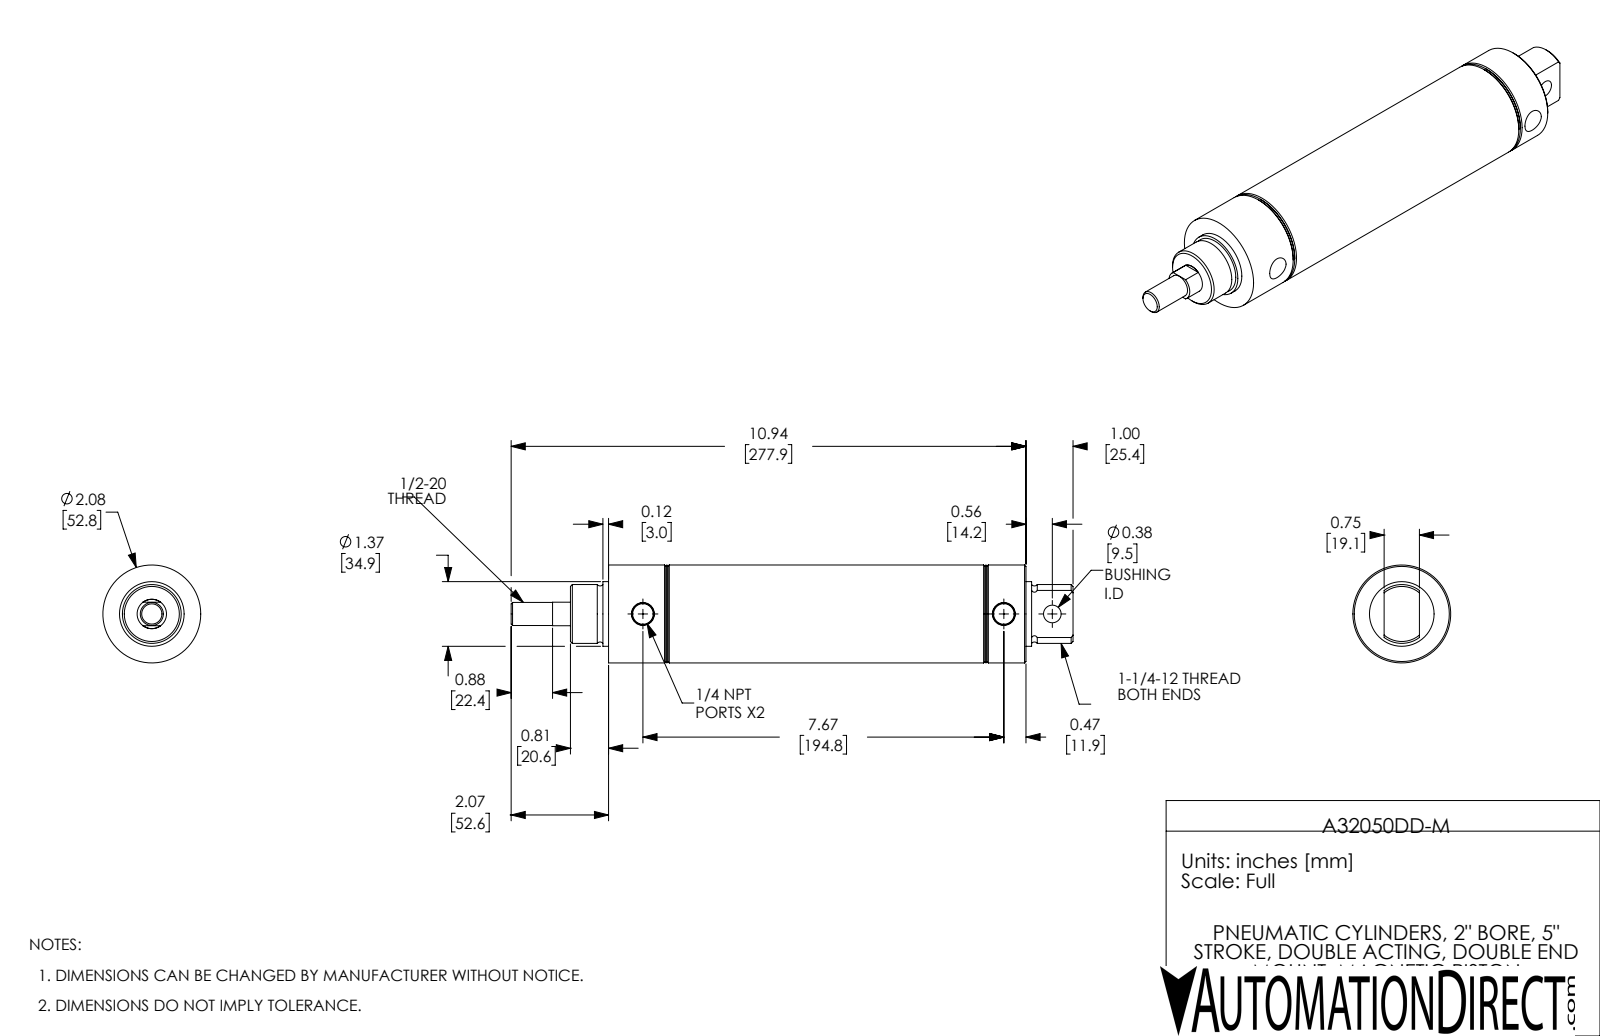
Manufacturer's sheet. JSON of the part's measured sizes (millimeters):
{"part_name": "A32050DD-M; A32050DD-M-Rod; A32050DD-M-MainBody", "step_written_by": "SolidWorks 2017 (AUTOMOTIVE_DESIGN)", "units": "millimeters", "bodies": {"solids": 2, "faces": 88, "planar": 20, "cylindrical": 30, "other": 38}, "overall_size": [303.3, 52.8, 52.8], "volume_mm3": 291700, "surface_area_mm2": 94320, "round_holes": [[11.1, 2], [9.5, 1], [15.9, 1], [50.8, 1]], "round_bosses_or_shafts": [[52.8, 1], [34.9, 1], [31.8, 1], [12.5, 1]], "face_to_face_distances": [42.8, 182.5, 12.7, 139.7, 127, 169.8, 55.5, 225.3, 3, 45.8], "hole_center_spacings": [26.2, 194.8, 221]}
